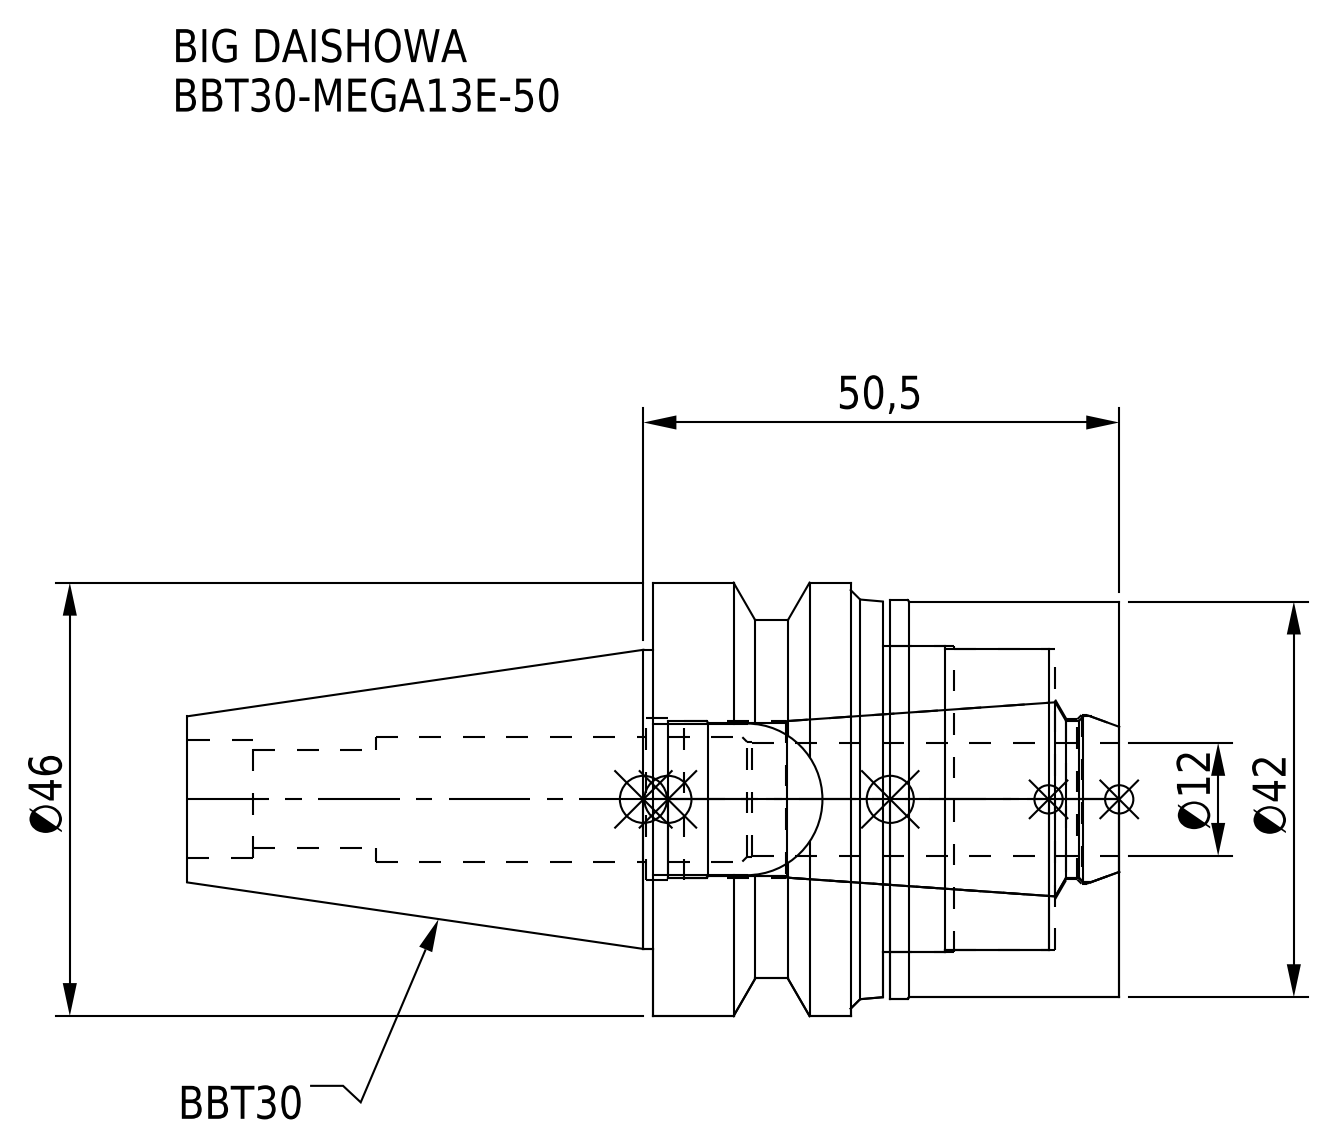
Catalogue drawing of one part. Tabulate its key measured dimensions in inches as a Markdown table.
| quantity | value |
| --- | --- |
| part name | BBT30ME13050-120_ASM.stp; BBT30-MEGA13E-50-120.stp; BBT30-MEGA13E-50-120-FreeParts; BBT30-MEGA13E-50 (+3 more) |
| STEP written by | SolidWorks 2019 (CONFIG_CONTROL_DESIGN) |
| units | inches |
| bodies | 2 solids, 78 faces (20 planar, 38 cylindrical, 20 other) |
| overall size | 3.894 × 1.811 × 1.811 |
| volume | 4.519 in³ |
| surface area | 37.38 in² |
| round holes (diameter × count) | 0.409 × 1, 0.492 × 1, 0.524 × 1, 0.654 × 1, 0.669 × 1, 0.677 × 1, 0.705 × 1, 1.26 × 1, 1.28 × 1 |
| round bosses / shafts (diameter × count) | 1.811 × 1, 1.665 × 1, 1.654 × 1, 1.25 × 1 |
| partial cylindrical surfaces (radius × count) | 0.317 × 1, 0.748 × 1 |
| main face-to-face distances | 1.949, 0.988, 0.957, 0.992, 0.031, 0.961, 0.028, 1.681, 0.268, 0.689 |
